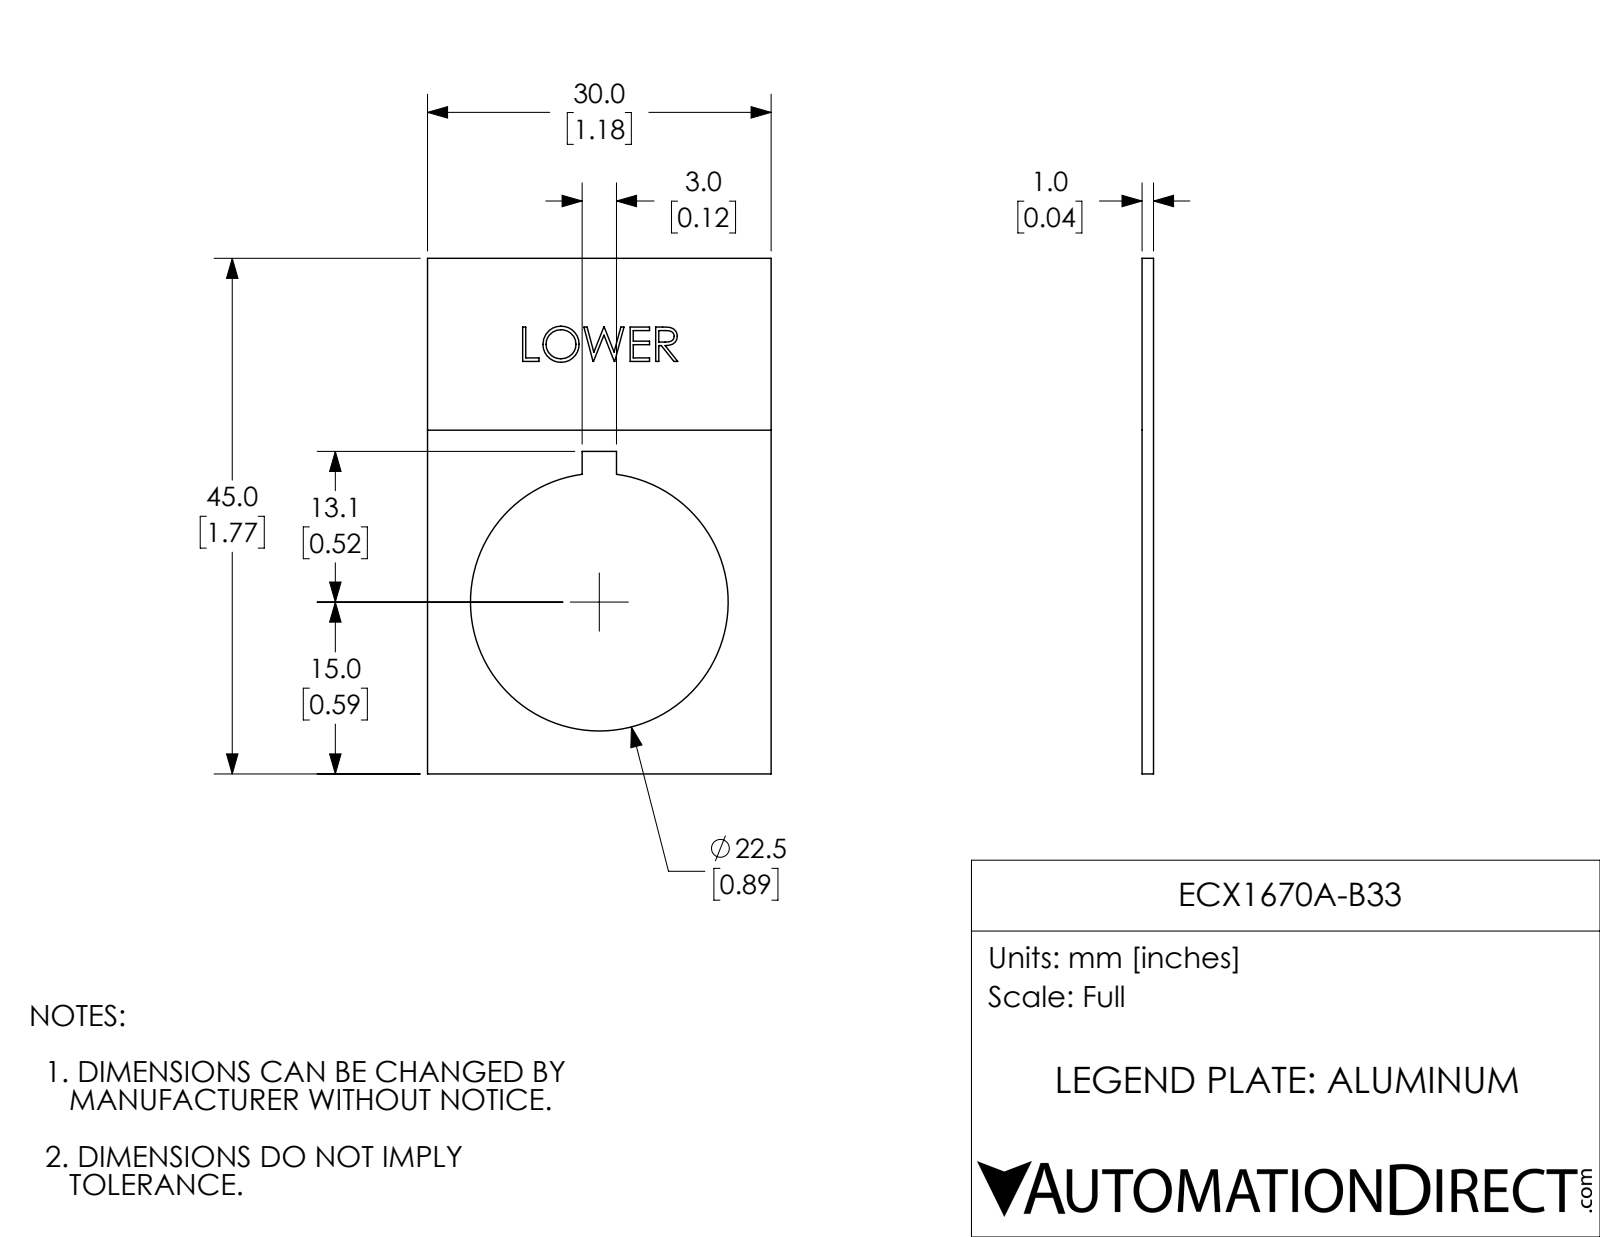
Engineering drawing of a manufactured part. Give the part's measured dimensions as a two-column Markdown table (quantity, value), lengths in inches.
| quantity | value |
| --- | --- |
| part name | ECX1670A-B33 |
| STEP written by | SolidWorks 2017 (AUTOMOTIVE_DESIGN) |
| units | inches |
| bodies | 1 solid, 75 faces (59 planar, 3 cylindrical, 13 other) |
| overall size | 1.772 × 1.181 × 0.039 |
| volume | 0.058 in³ |
| surface area | 3.286 in² |
| round holes (diameter × count) | 0.886 × 1 |
| main face-to-face distances | 0.039, 1.181, 1.772, 0.038, 0.531, 0.65, 1.108, 0.663, 0.118, 0.012 |
